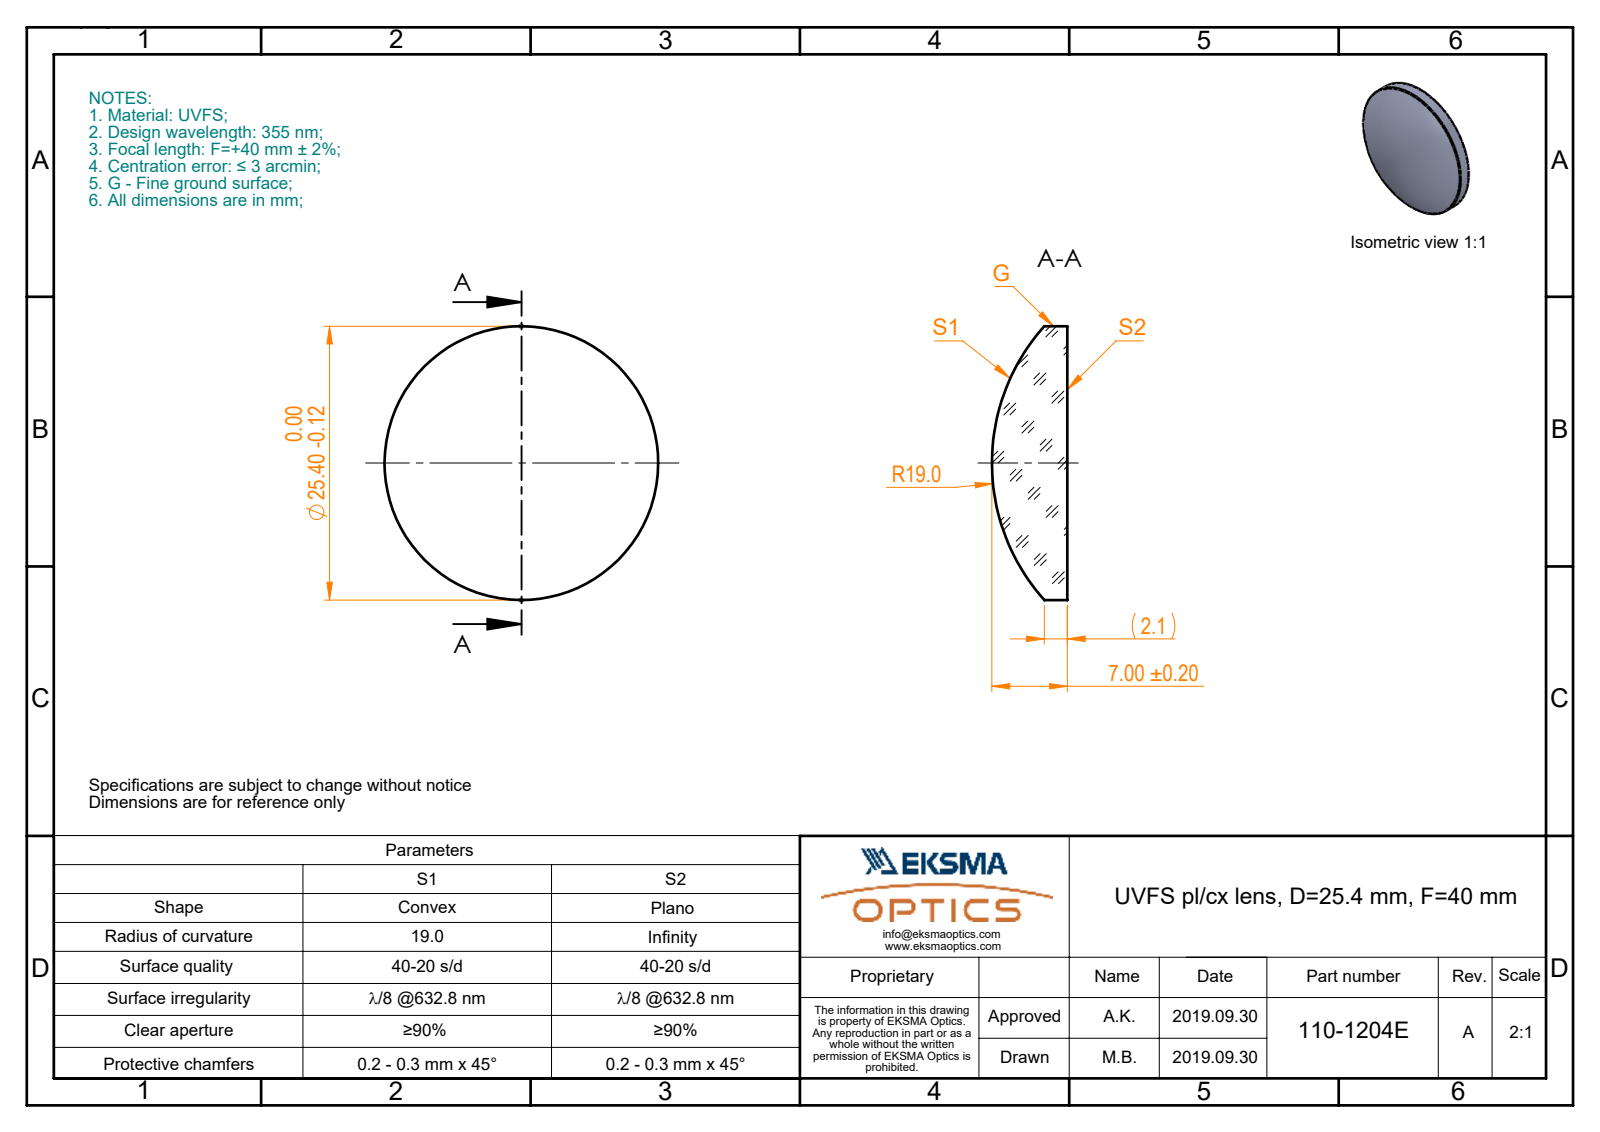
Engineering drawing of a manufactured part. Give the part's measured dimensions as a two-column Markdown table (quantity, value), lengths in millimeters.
| quantity | value |
| --- | --- |
| part name | 110-1204E UVFS pl-cx 25.4 F40 |
| STEP written by | SolidWorks 2019 (CONFIG_CONTROL_DESIGN) |
| units | millimeters |
| bodies | 1 solid, 4 faces (1 planar, 2 cylindrical, 1 other) |
| overall size | 25.4 × 25.4 × 7 |
| volume | 2 377 mm³ |
| surface area | 1 259 mm² |
| round bosses / shafts (diameter × count) | 25.4 × 1 |
